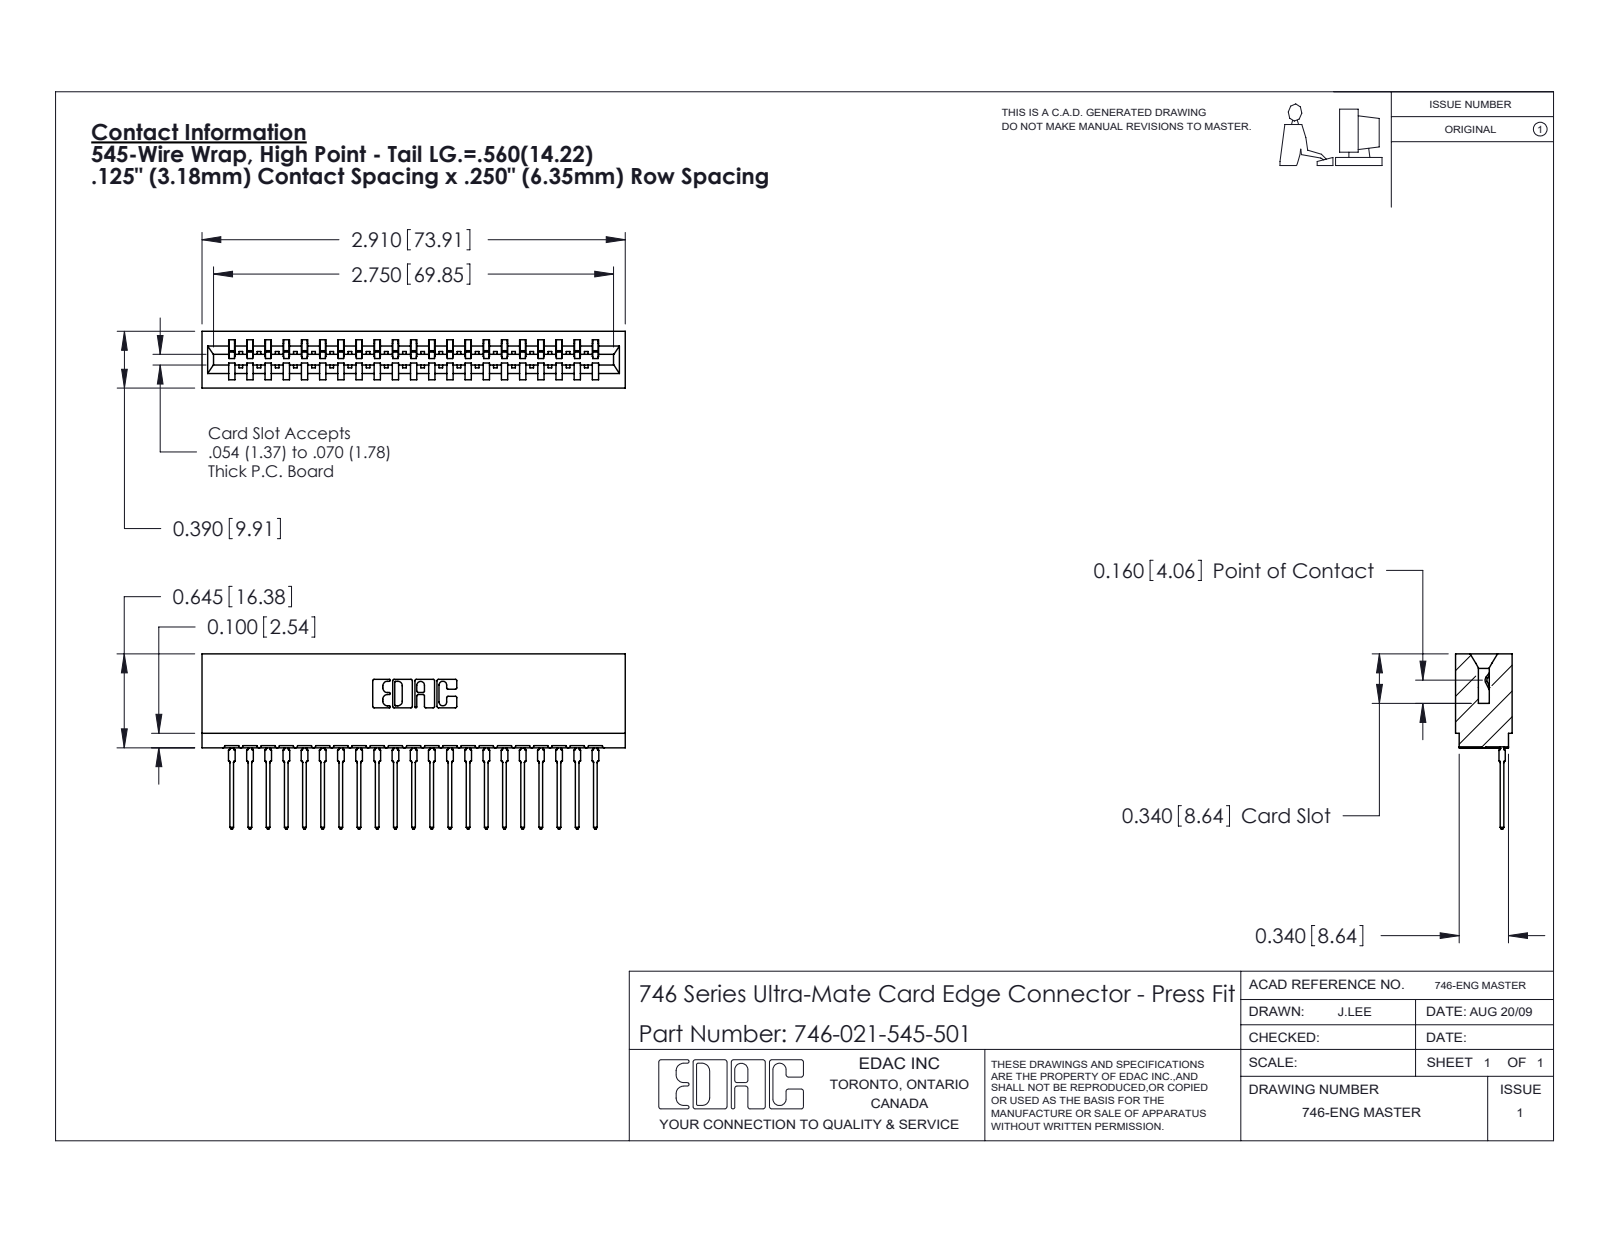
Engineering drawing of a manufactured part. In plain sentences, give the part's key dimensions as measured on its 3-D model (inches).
The part is named "746-292-001_545; 746 Part_.340 Slot Depth - 01; 746-021-545-501". Its 3-D file was written by "SolidWorks 2020 (CONFIG_CONTROL_DESIGN)". It is 22 solids with 2365 faces: 1378 planar, 441 cylindrical and 546 other. Overall it measures 2.91 by 1.204 by 0.39 inches. Its volume is 0.518 cubic inches and its surface area 17.7 square inches. Partial cylindrical surfaces (rounded edges, fillets, slot ends): 42 of radius 0.021, 22 of radius 0.01, 22 of radius 0.015, 6 of radius 0.007, 6 of radius 0.031, 4 of radius 0.005, 4 of radius 0.011, 3 of radius 0.026. The main face-to-face distances are 0.25, 0.057, 0.333, 0.39, 0.5, 0.025, 0.307, 0.125, 0.292, 0.125.
